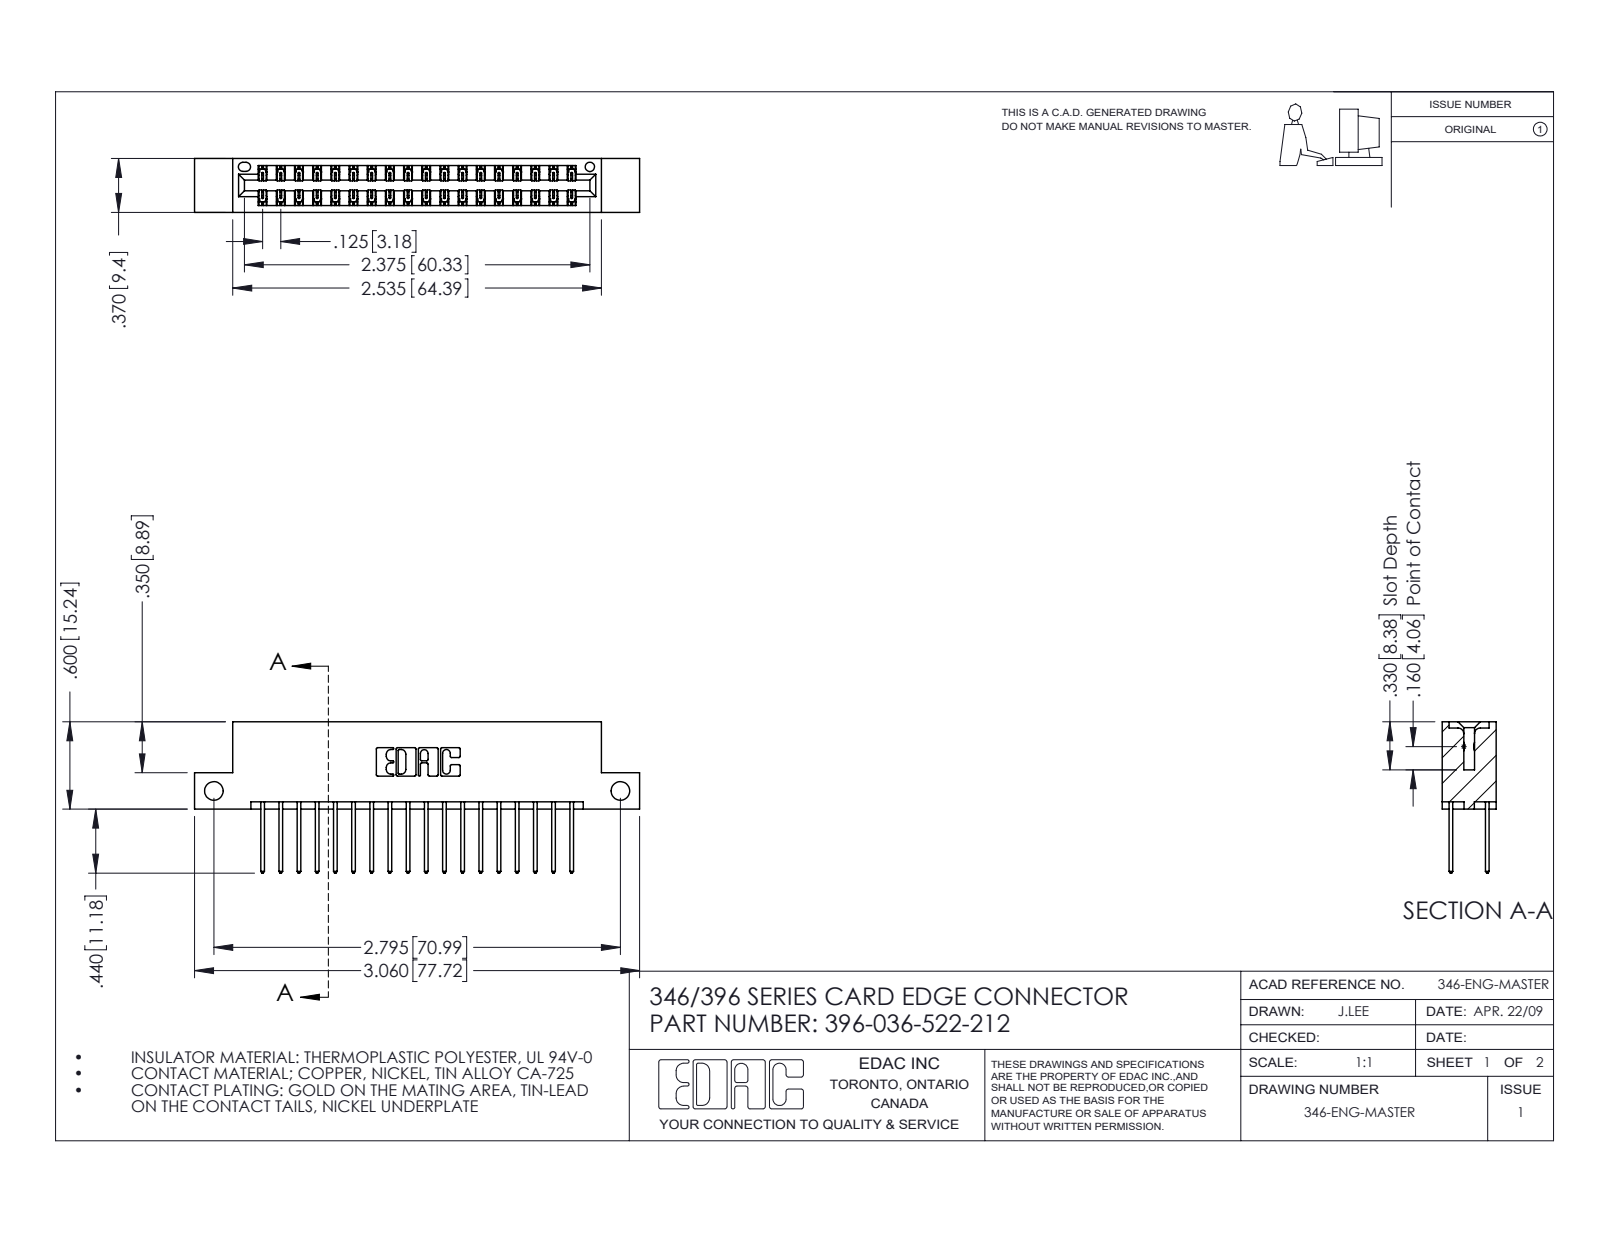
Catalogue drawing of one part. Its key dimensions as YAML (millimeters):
part_name: "345-292-001_345-293-122; 396-036-522-212; 346 Part_Flush Mounting Lugs - Side Mount"
step_written_by: "SolidWorks 2016 (CONFIG_CONTROL_DESIGN)"
units: millimeters
bodies: {solids: 37, faces: 1994, planar: 1336, cylindrical: 658, other: 0}
overall_size: [77.7, 26.4, 9.4]
volume: 7390
surface_area: 10080
round_holes:
  - {diameter: 3.3, count: 2}
  - {diameter: 1.6, count: 1}
partial_cylinders:
  - {radius: 0.2, count: 54}
  - {radius: 0.3, count: 36}
  - {radius: 0.3, count: 22}
  - {radius: 0.2, count: 6}
  - {radius: 0.8, count: 6}
  - {radius: 0.7, count: 3}
  - {radius: 0.4, count: 2}
  - {radius: 0.6, count: 2}
face_to_face_distances: [1.2, 8.2, 6.4, 9.4, 1.8, 7.6, 0.6, 7, 3.8, 5.6]
hole_center_spacings: [71]
